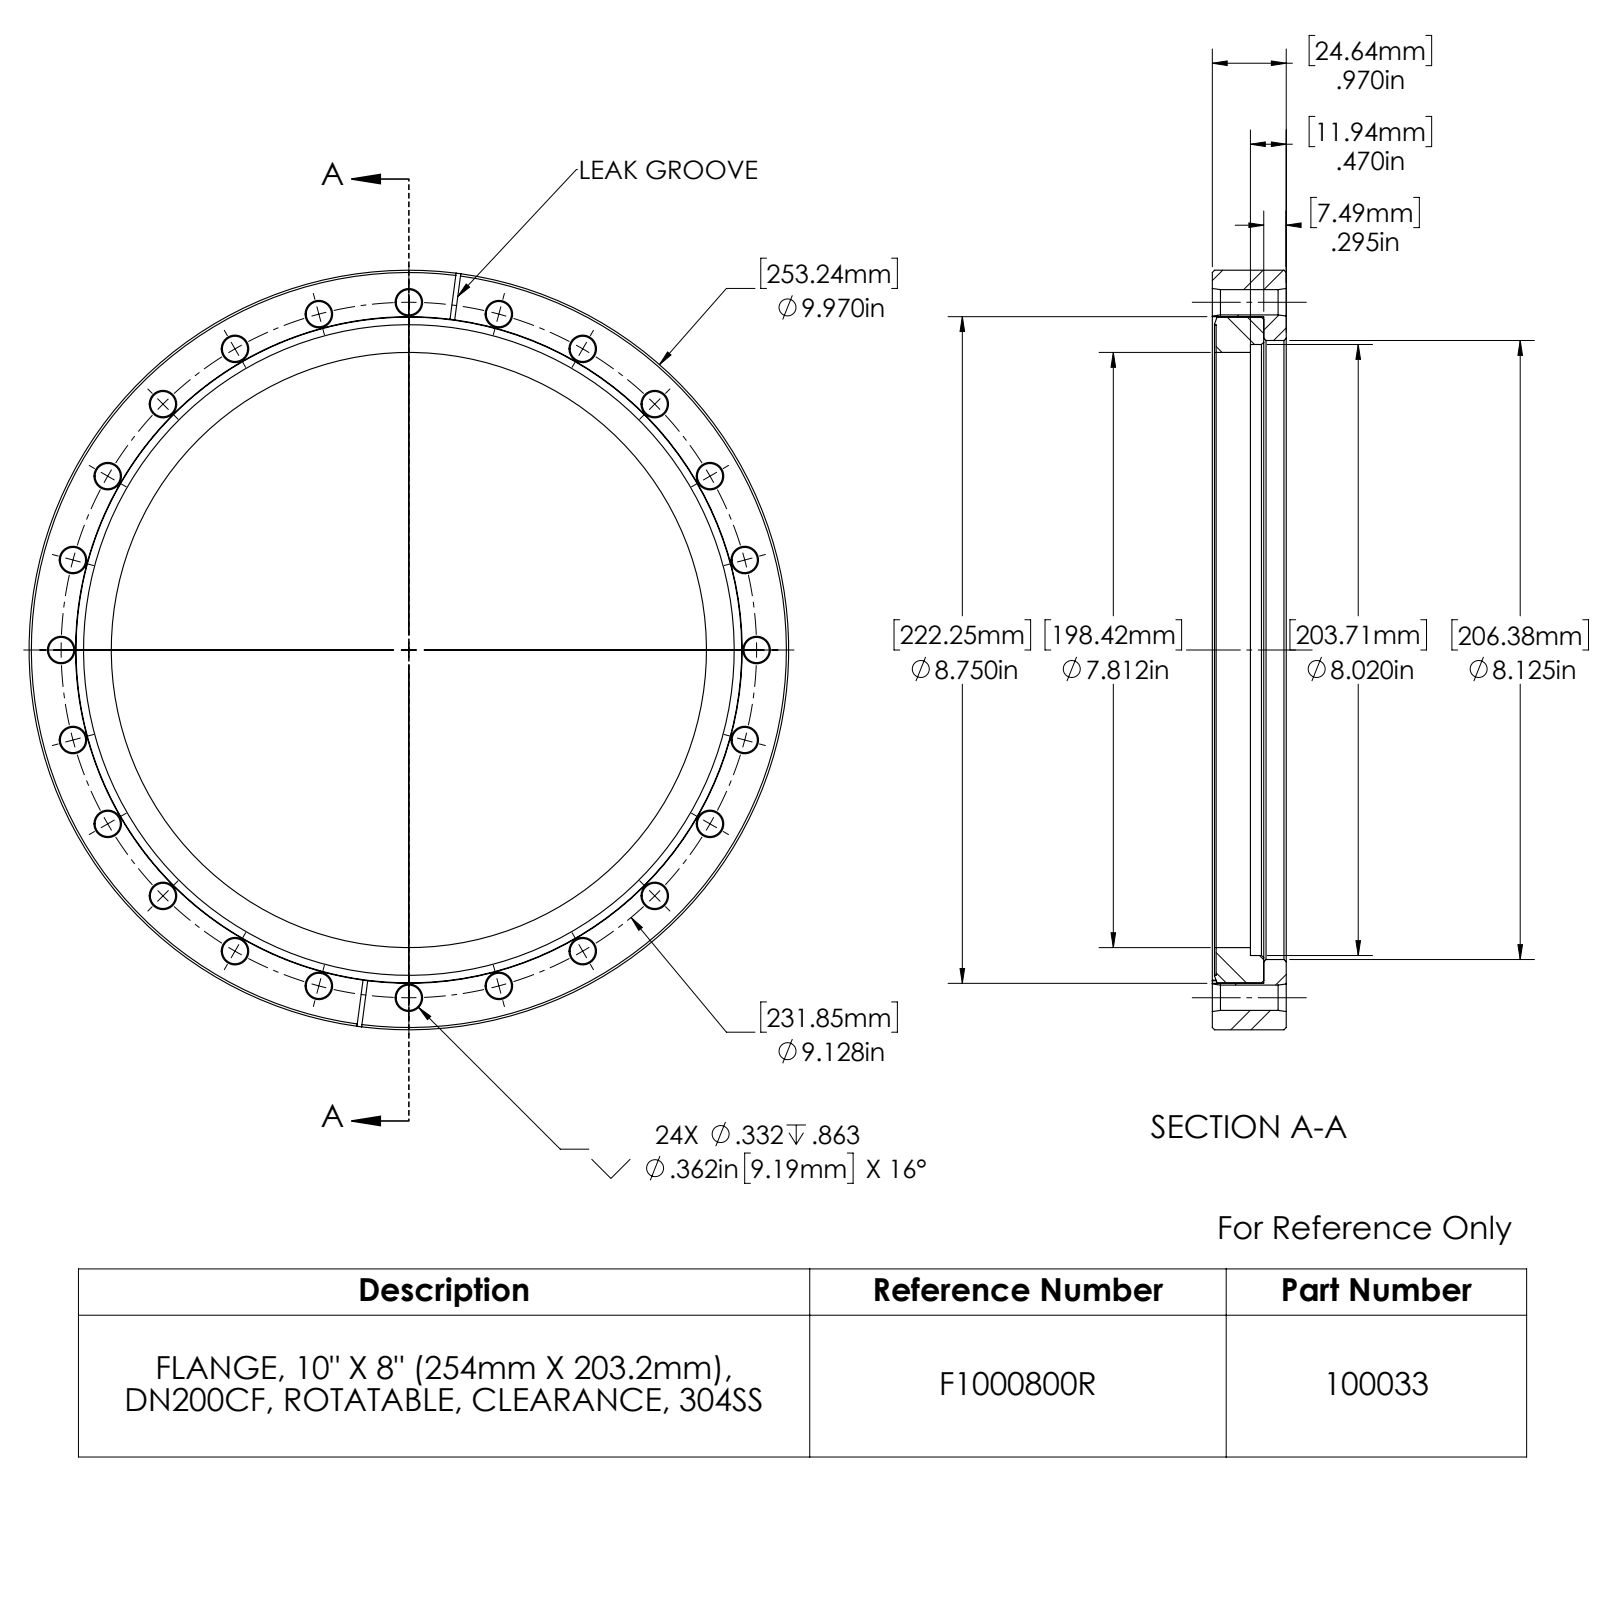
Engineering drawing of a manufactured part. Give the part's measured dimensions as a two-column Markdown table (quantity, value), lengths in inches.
| quantity | value |
| --- | --- |
| part name | 100033_A; 915009; 910033 |
| STEP written by | SolidWorks 2022 (CONFIG_CONTROL_DESIGN) |
| units | inches |
| bodies | 2 solids, 197 faces (13 planar, 62 cylindrical, 122 other) |
| overall size | 9.97 × 9.97 × 0.97 |
| volume | 24.79 in³ |
| surface area | 182.6 in² |
| round holes (diameter × count) | 0.332 × 24, 7.812 × 1, 8.02 × 1, 8.125 × 1, 8.54 × 1, 8.75 × 1 |
| round bosses / shafts (diameter × count) | 9.97 × 1, 8.738 × 1 |
| main face-to-face distances | 0.295, 0.675, 0.97, 0.05, 0.625, 0.92, 0.5, 0.45, 0.175, 0.47 |
| hole center spacings | 4.564, 4.564, 8.433, 9.05, 5.557, 7.242, 7.905, 8.817 |
